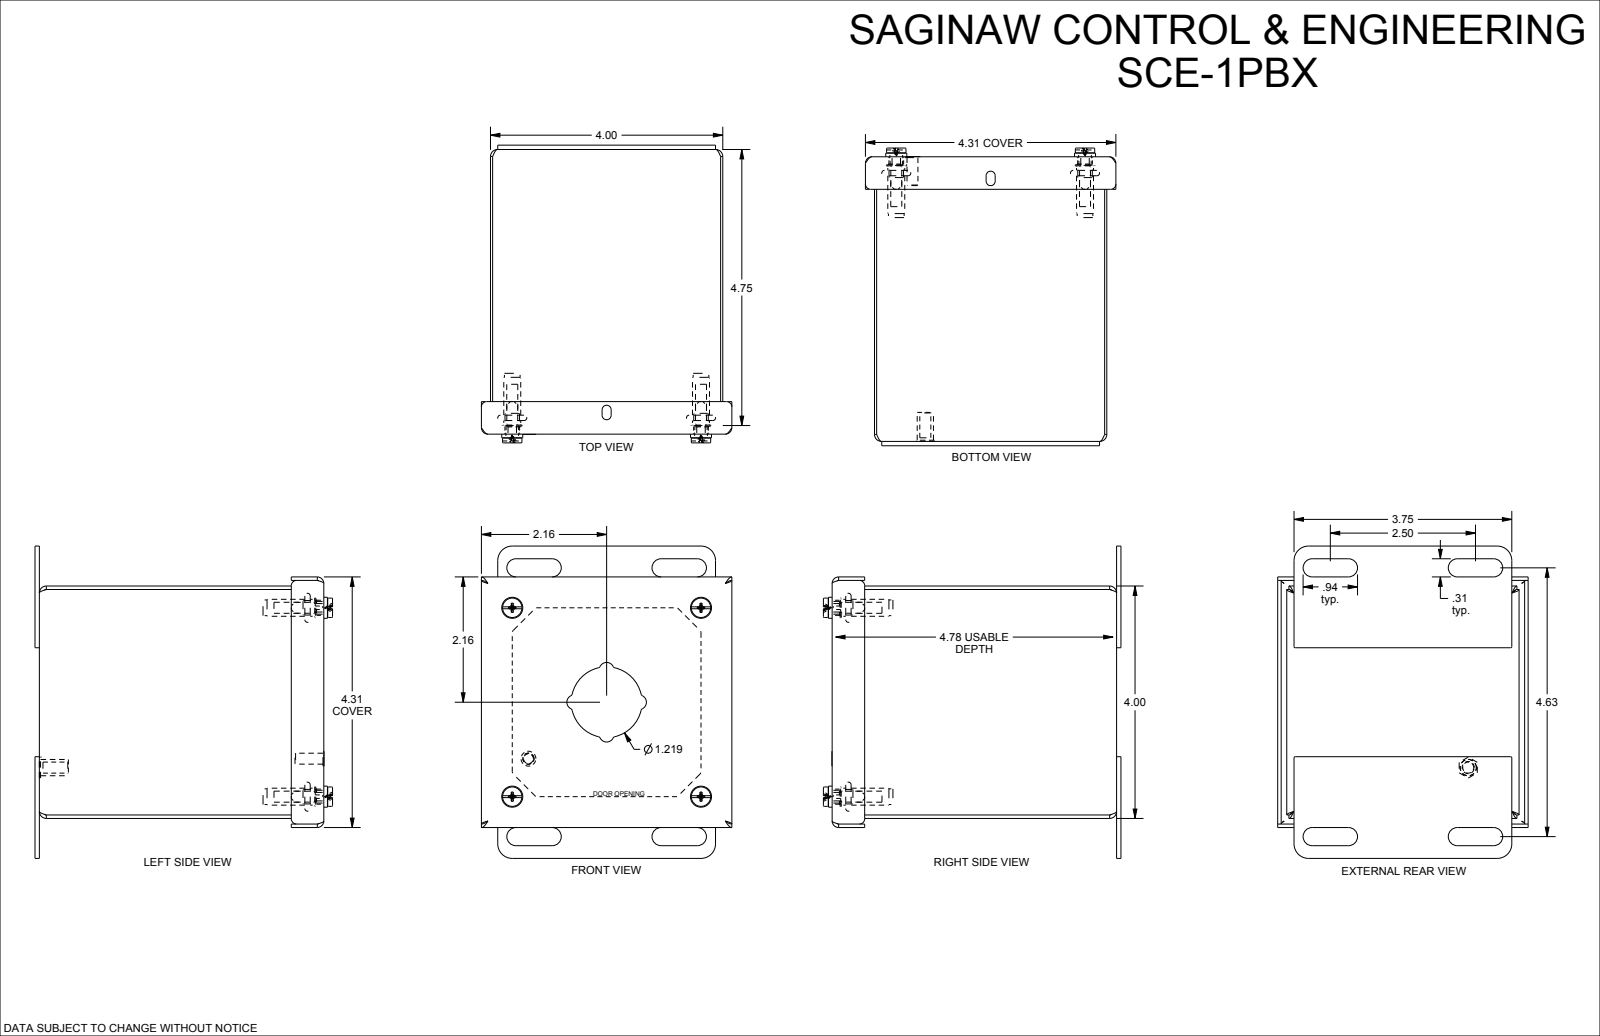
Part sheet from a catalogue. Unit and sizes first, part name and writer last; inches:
Units: inches
Overall size (bounding box): 5.375 × 5.124 × 4.313
Round holes (diameter × count): ⌀0.19 ×5, ⌀0.22 ×4, ⌀0.25 ×4, ⌀0.25 ×4, ⌀0.317 ×4, ⌀0.193 ×1
Round bosses / shafts (diameter × count): ⌀0.188 ×5, ⌀0.437 ×4, ⌀0.362 ×4, ⌀0.34 ×4, ⌀0.334 ×4, ⌀0.292 ×4, ⌀0.27 ×4, ⌀0.26 ×4
Partial cylindrical surfaces — rounded edges, fillets, slot ends (radius × count): R0.06 ×12, R0.015 ×8, R0.04 ×8, R0.063 ×8, R0.115 ×8, R0.156 ×8, R0.245 ×8, R0.02 ×4
Main face-to-face distances: 0.06, 3.94, 4, 3.88, 4.838, 4.898, 0.156, 4.096, 4.778, 0.075
Hole centre spacings: 3.25, 4.596, 3.25, 3.25, 2.795, 0.707, 0.711, 2.611
Volume: 8.677 in³ · Surface area: 287.7 in²
Bodies: 19 solids, 528 faces (205 planar, 161 cylindrical, 162 other)
Part name (STEP PRODUCT): SCE-1PBX-RAL1018
STEP written by: SolidWorks 2021 (AUTOMOTIVE_DESIGN)
